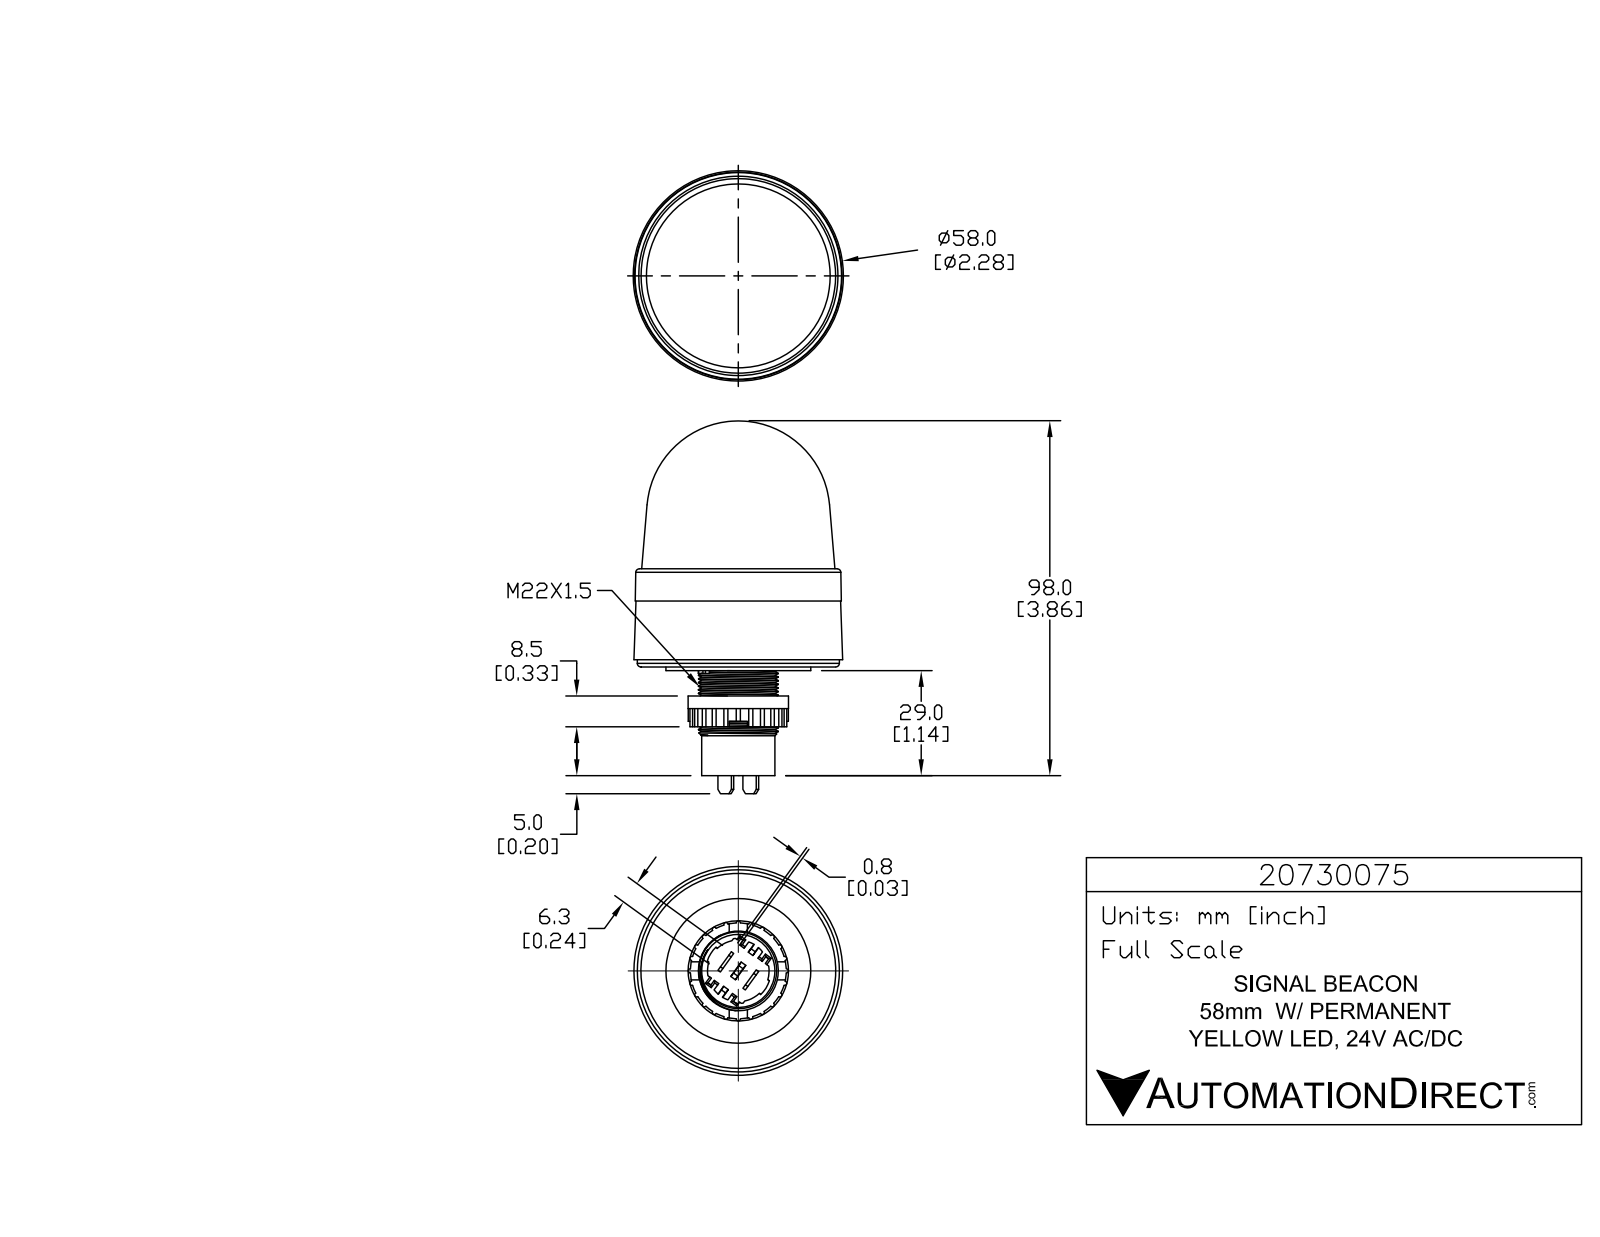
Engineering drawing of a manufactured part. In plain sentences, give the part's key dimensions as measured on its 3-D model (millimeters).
The part is named "20730075". Its 3-D file was written by "SolidWorks 2015 (AUTOMOTIVE_DESIGN)". It is 1 solid with 266 faces: 119 planar, 120 cylindrical and 27 other. Overall it measures 102.9 by 57.6 by 57.6 millimeters. Its volume is 147 700 cubic millimeters and its surface area 20 030 square millimeters. Round holes: 1 of diameter 23. Round bosses or shafts: 1 of diameter 55.8, 1 of diameter 40, 1 of diameter 27.7, 1 of diameter 22, 1 of diameter 20.2. Partial cylindrical surfaces (rounded edges, fillets, slot ends): 24 of radius 0.6, 2 of radius 0.5, 1 of radius 8.5, 1 of radius 9, 1 of radius 13.3. The main face-to-face distances are 1, 7, 3, 29, 8.5, 8, 27, 19, 26, 18.5.
